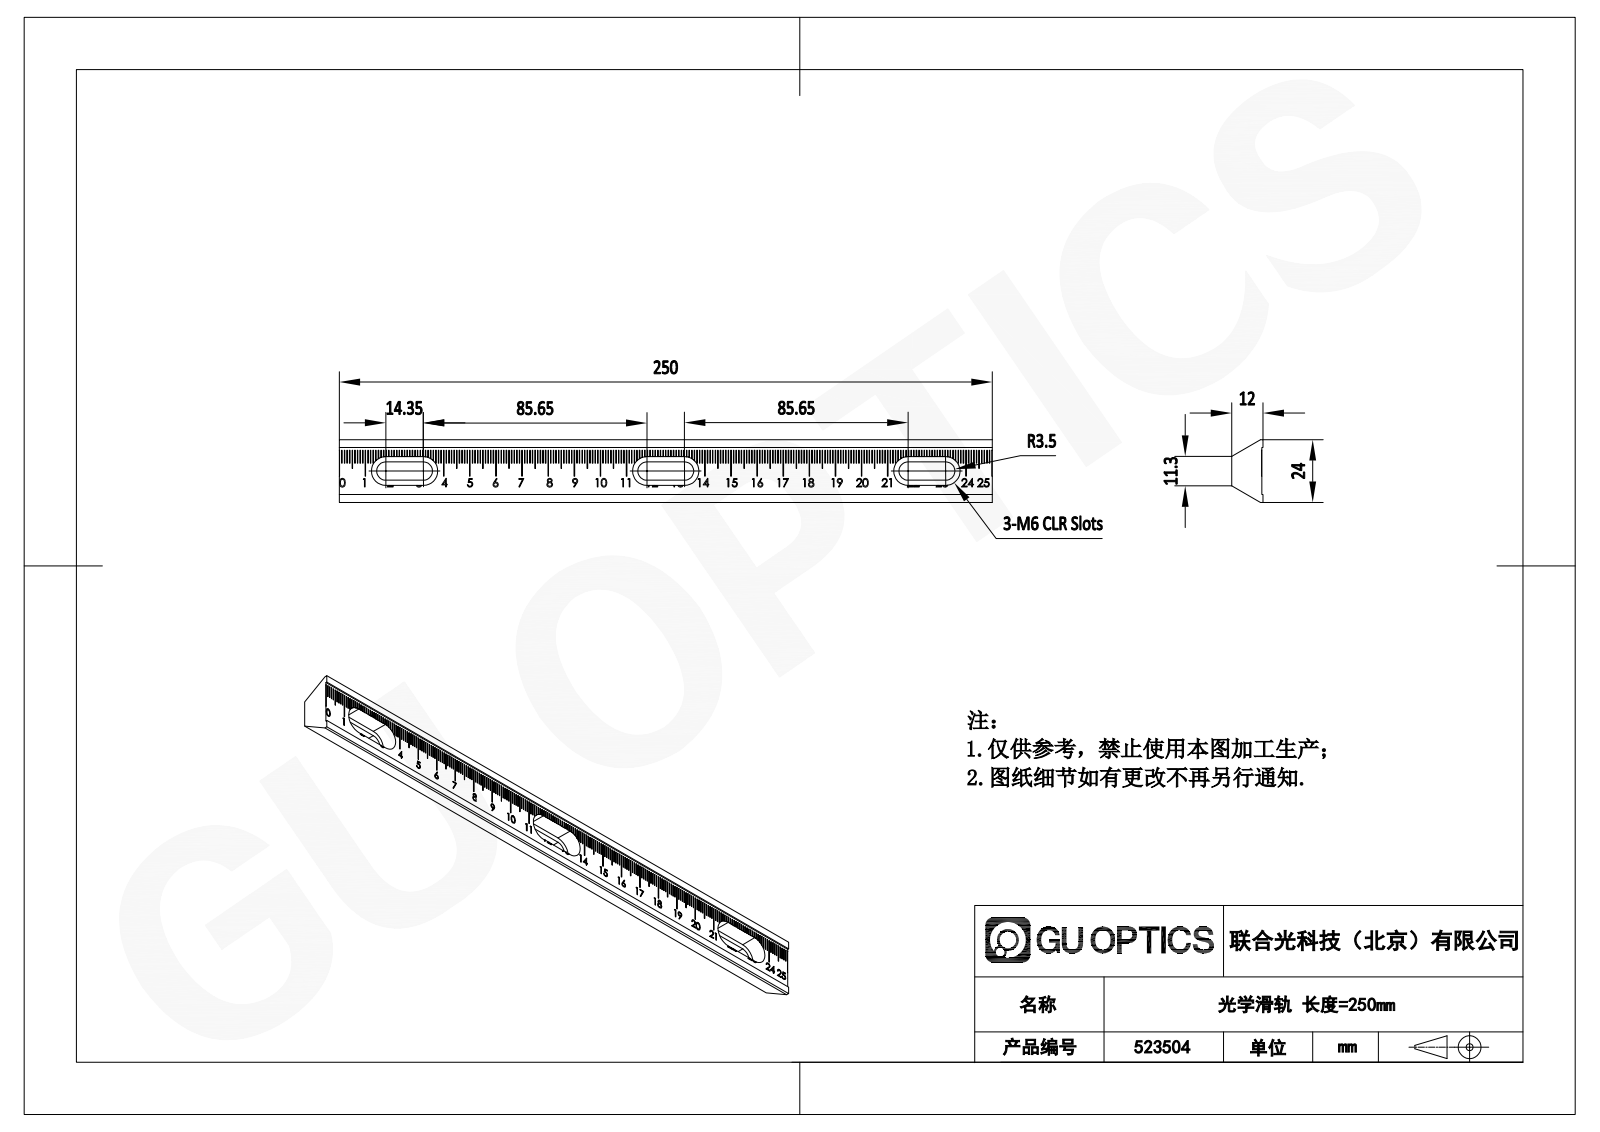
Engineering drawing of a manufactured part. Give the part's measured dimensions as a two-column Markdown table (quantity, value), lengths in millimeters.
| quantity | value |
| --- | --- |
| part name | ORE-25 |
| STEP written by | SolidWorks 2012 (CONFIG_CONTROL_DESIGN) |
| units | millimeters |
| bodies | 1 solid, 1644 faces (1472 planar, 12 cylindrical, 160 other) |
| overall size | 250 × 24 × 12 |
| volume | 45 254 mm³ |
| surface area | 17 508 mm² |
| partial cylindrical surfaces (radius × count) | 3.5 × 6, 5.5 × 6 |
| main face-to-face distances | 11.5, 0.5, 12, 6.5, 7, 17.5, 8.5, 9, 2, 15.5 |
